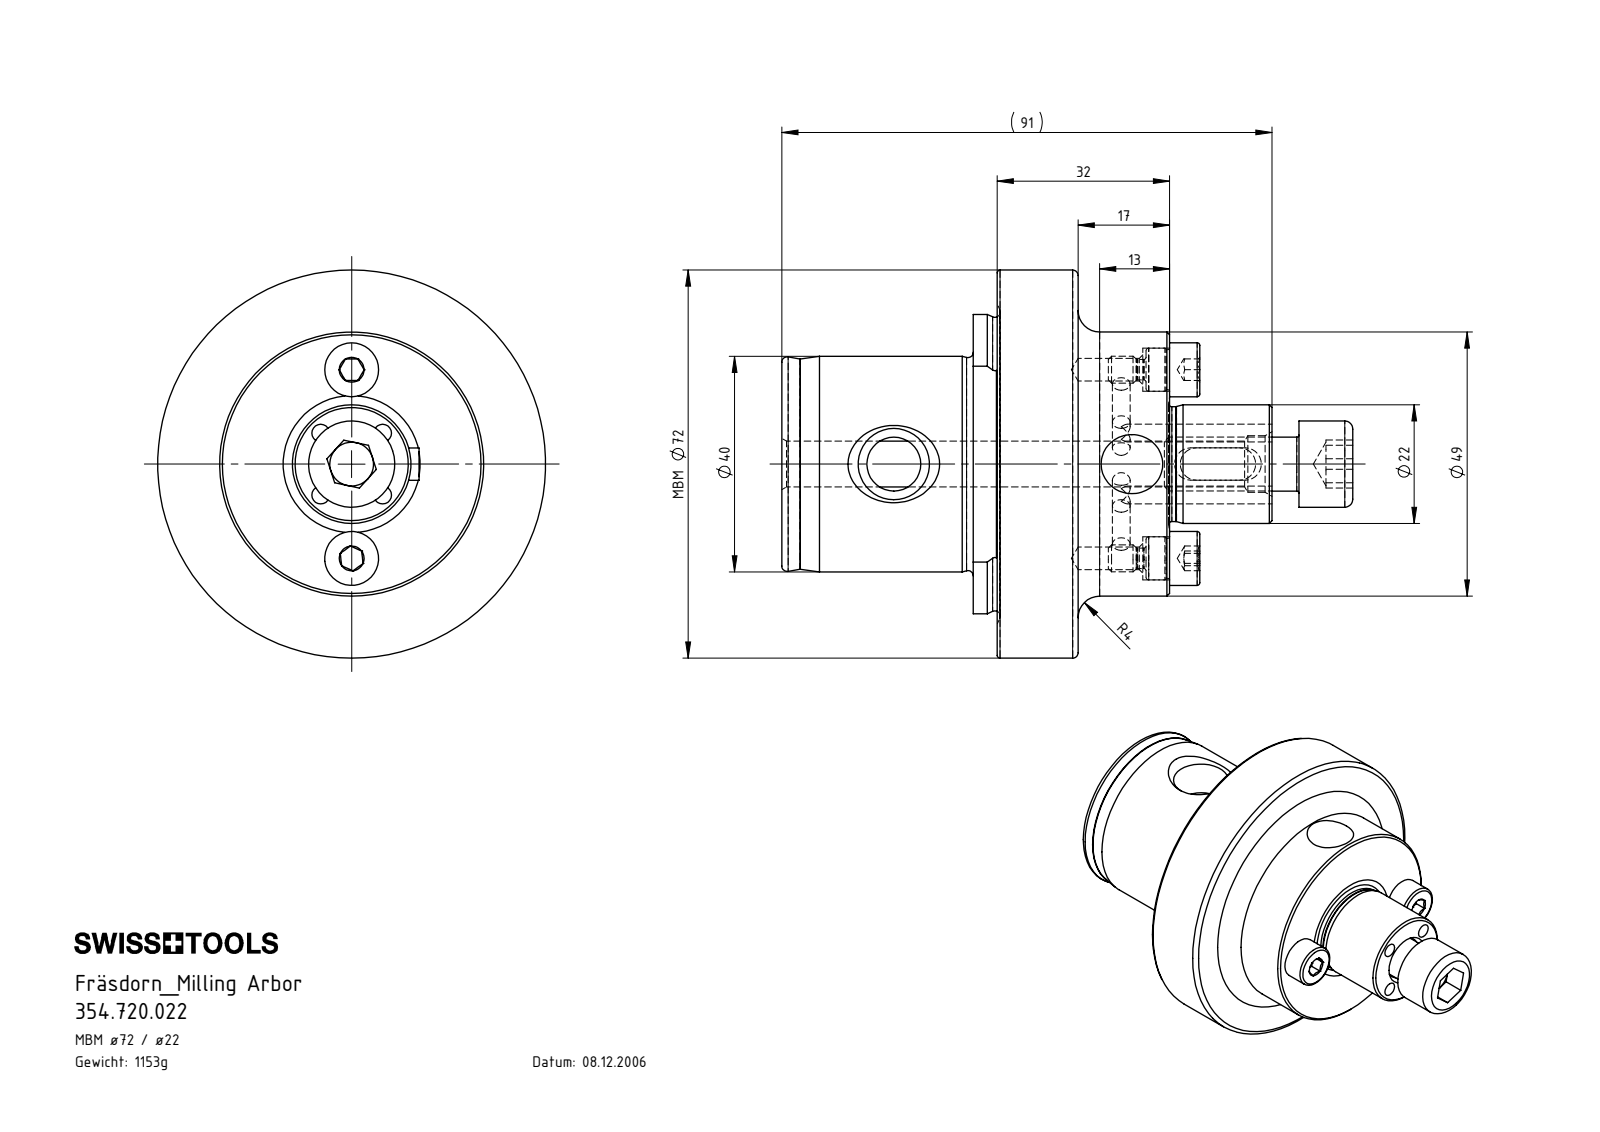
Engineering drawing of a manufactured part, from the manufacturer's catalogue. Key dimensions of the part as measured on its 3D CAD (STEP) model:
Part name (STEP PRODUCT): MB7-D22.K01.032_C; ISO 4762 - M4 x 10; D22-ER1.K63.016_A; D22-ER1.K62.008_A (+4 more)
STEP written by: SolidWorks 2017 (CONFIG_CONTROL_DESIGN)
Units: millimetres
Bodies: 8 solids, 359 faces (79 planar, 145 cylindrical, 135 other)
Overall size (bounding box): 106 × 72 × 72
Volume: 153 146 mm³ · Surface area: 30 857 mm²
Round holes (diameter × count): ⌀2.5 ×12, ⌀3.3 ×4, ⌀4.5 ×1, ⌀8 ×1, ⌀8.5 ×1, ⌀10 ×1, ⌀10.5 ×1, ⌀15 ×1
Round bosses / shafts (diameter × count): ⌀72 ×1, ⌀49 ×1, ⌀40 ×1, ⌀28 ×1, ⌀22 ×1, ⌀21.3 ×1, ⌀16 ×1, ⌀10 ×1
Partial cylindrical surfaces — rounded edges, fillets, slot ends (radius × count): R3 ×4, R5 ×1, R27.77 ×1
Main face-to-face distances: 15, 32, 17, 40, 55, 72, 35.55, 4.45, 19.45, 36.45
Hole centre spacings: 10, 17.32, 19.99, 4.43, 5.62, 8.13, 12.41, 13.34
